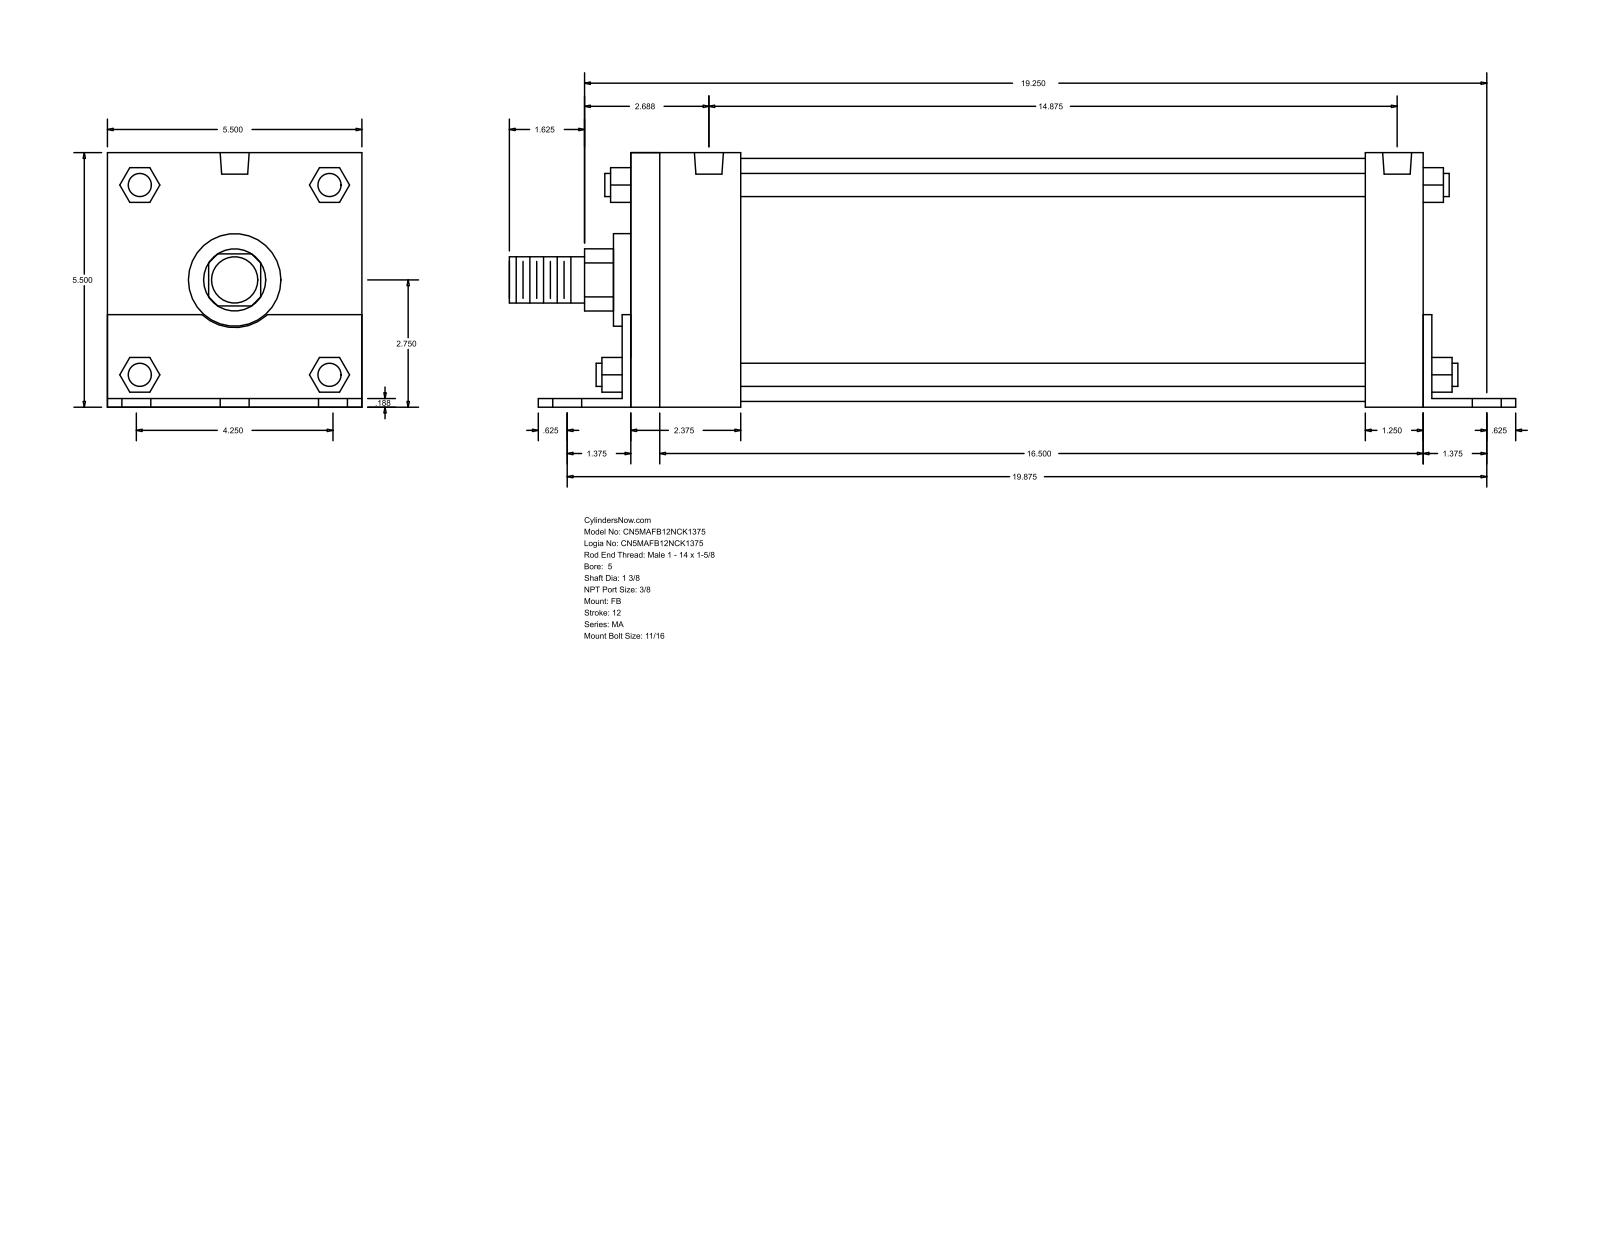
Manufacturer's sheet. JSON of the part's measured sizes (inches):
{"part_name": "MA_FB__0500_1.375", "step_written_by": "GSSL Pune (CONFIG_CONTROL_DESIGN)", "units": "inches", "bodies": {"solids": 0, "faces": 140, "planar": 105, "cylindrical": 35, "other": 0}, "overall_size": [21.75, 5.502, 5.5], "round_holes": [[0.687, 6], [0.437, 4], [0.627, 2]], "round_bosses_or_shafts": [[0.5, 4], [5.25, 1], [2, 1], [1.375, 1], [1, 1]], "partial_cylinders_radius": [[0.672, 1], [1.03, 1]], "face_to_face_distances": [5.5, 0.187, 5.502, 17.313, 0.185, 5.315, 17.125, 17.5, 1.438, 2.562], "hole_center_spacings": [2.125, 19.989, 19.875, 0.188, 2.876, 3.006, 3.728, 3.883]}
